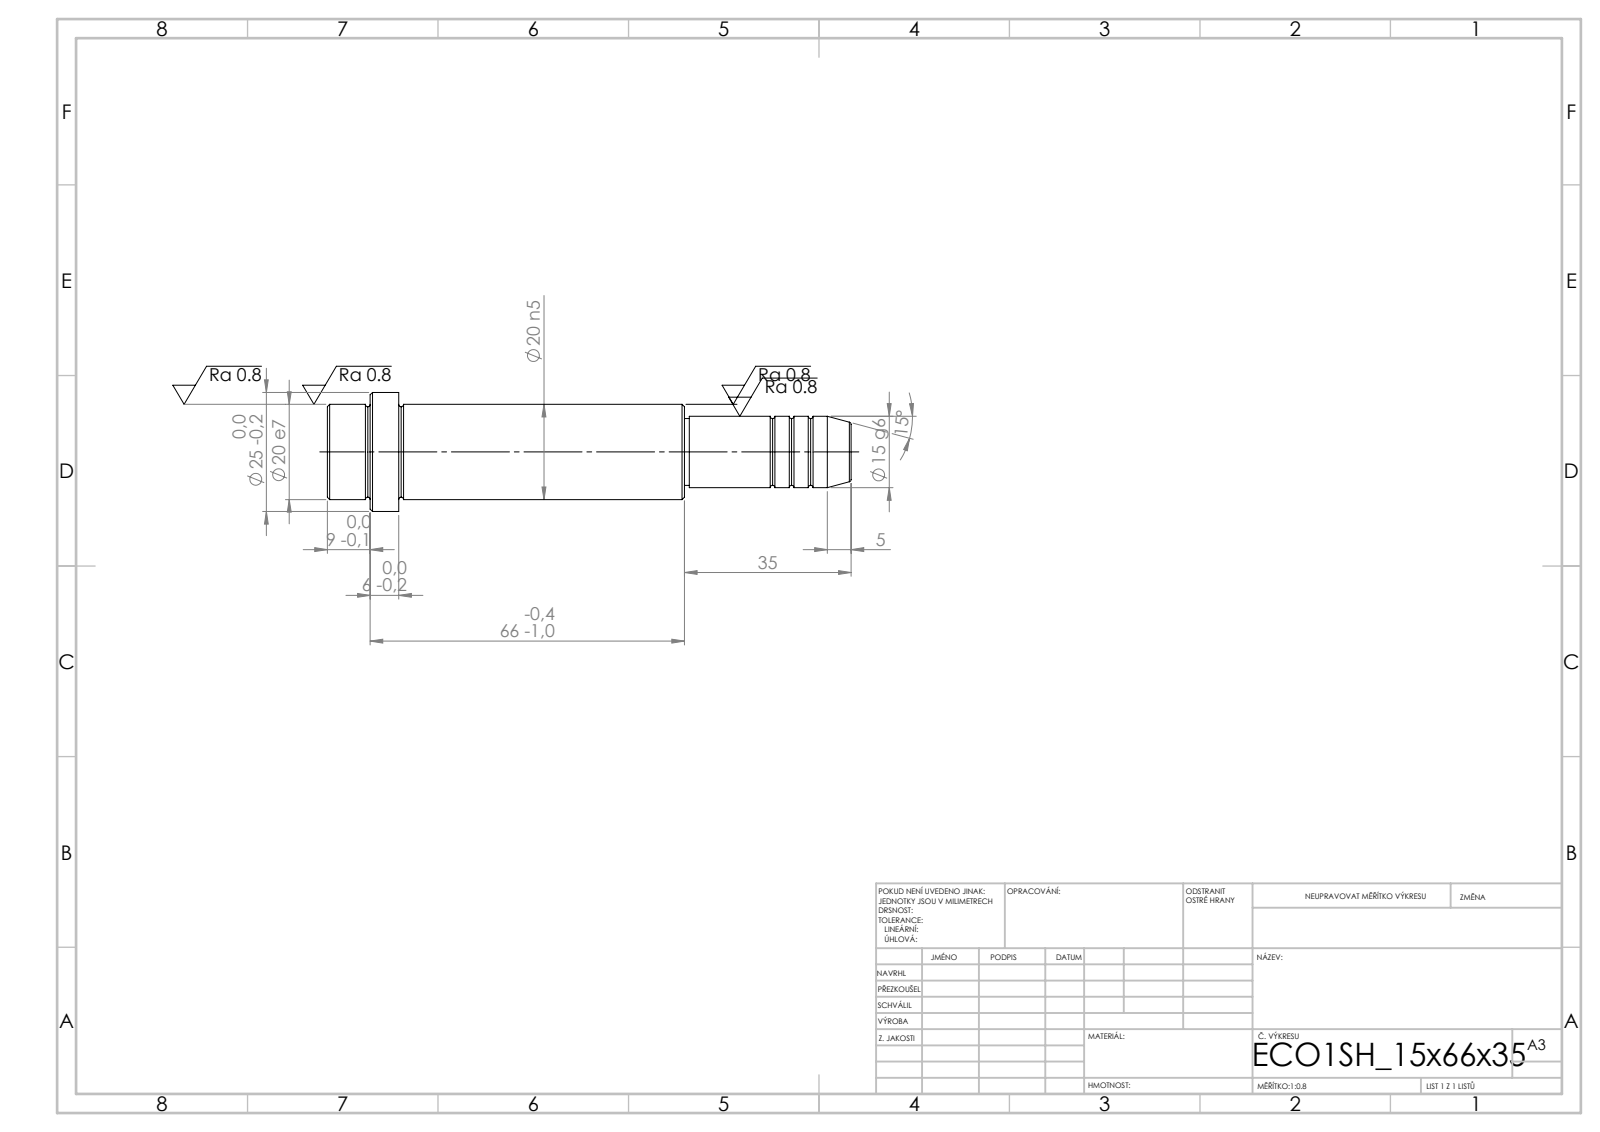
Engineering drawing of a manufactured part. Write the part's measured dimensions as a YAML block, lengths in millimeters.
step_written_by: "SolidWorks 2019 (CONFIG_CONTROL_DESIGN)"
units: millimeters
bodies: {solids: 1, faces: 52, planar: 6, cylindrical: 16, other: 30}
overall_size: [110, 25, 25]
volume: 30508
surface_area: 7481
round_bosses_or_shafts:
  - {diameter: 25, count: 1}
  - {diameter: 20, count: 1}
  - {diameter: 15, count: 1}
  - {diameter: 14, count: 1}
face_to_face_distances: [15, 6, 9, 60, 66, 75, 35, 95, 101, 110]
